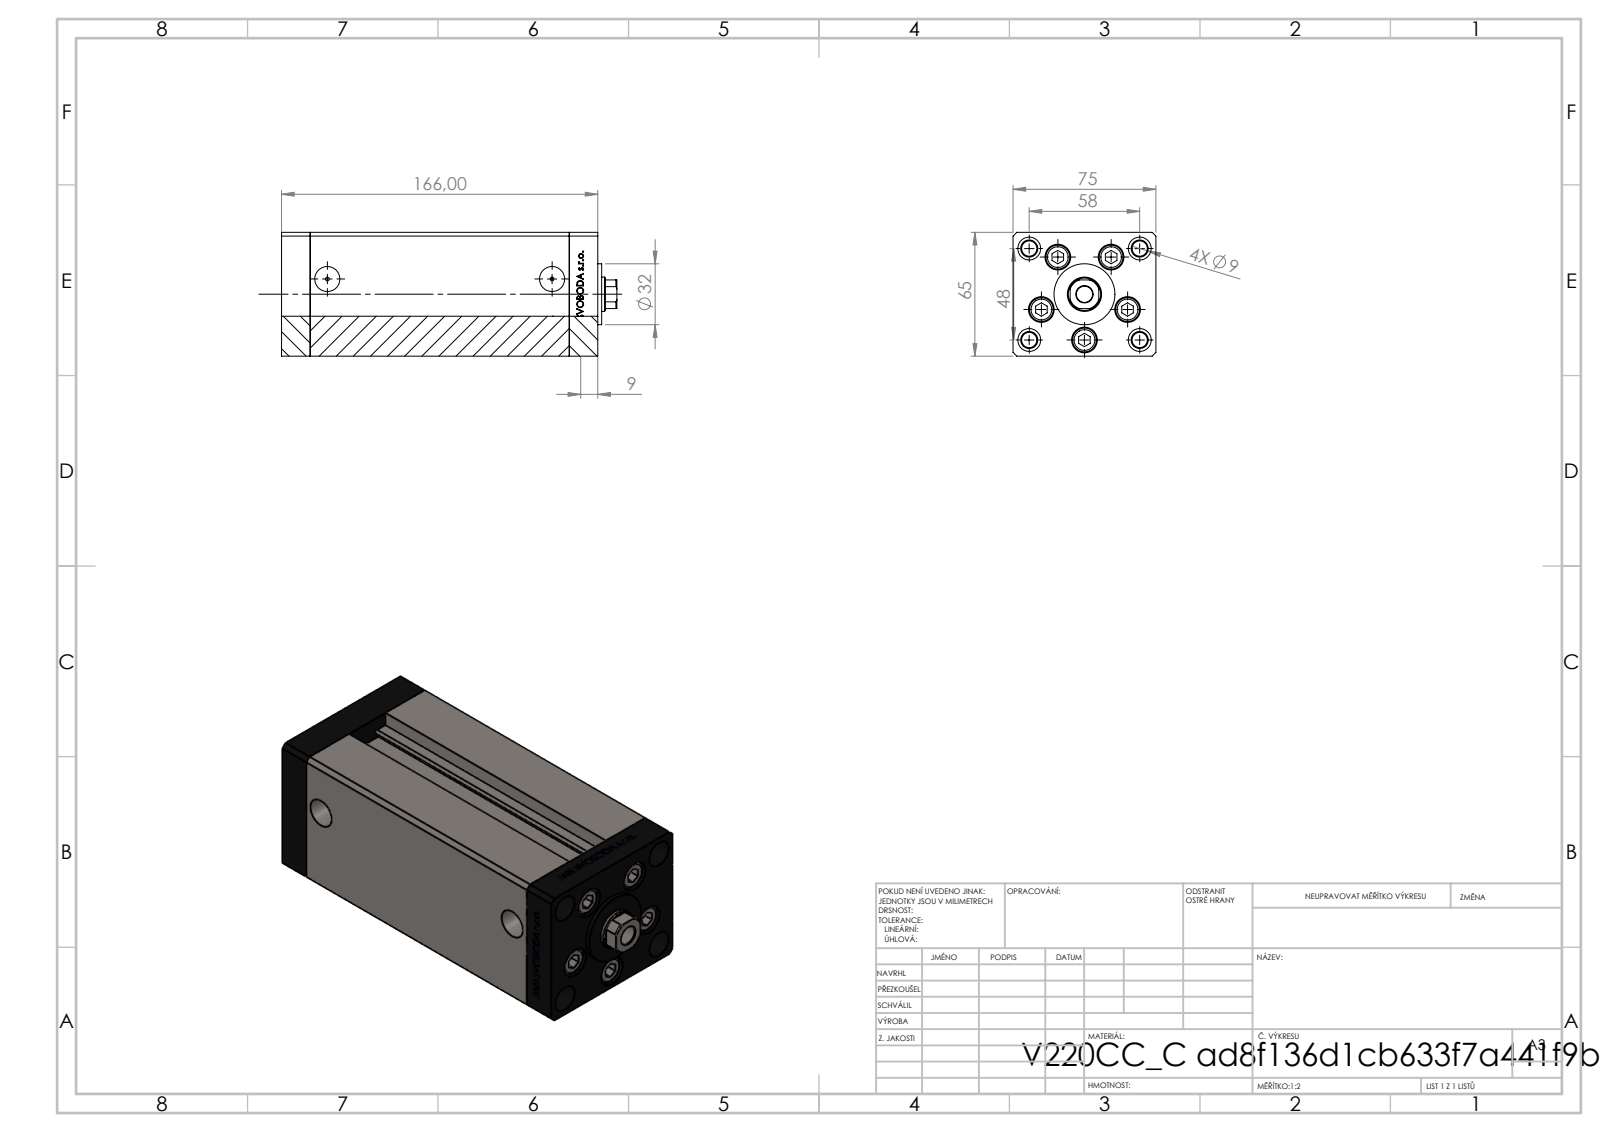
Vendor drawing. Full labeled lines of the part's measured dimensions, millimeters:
Part name (STEP PRODUCT): V220C FRONT; V220C_C MIDDLE; V220C_VC_C; V220C BACK_C (+1 more)
STEP written by: SolidWorks 2019 (CONFIG_CONTROL_DESIGN)
Units: millimetres
Bodies: 13 solids, 1169 faces (540 planar, 167 cylindrical, 462 other)
Overall size (bounding box): 176 × 75 × 65
Volume: 680 499 mm³ · Surface area: 142 517 mm²
Round holes (diameter × count): ⌀9 ×9, ⌀13.5 ×5, ⌀8 ×4, ⌀12 ×4, ⌀2 ×2, ⌀13.16 ×2, ⌀8.5 ×1, ⌀12.5 ×1, ⌀18 ×1
Round bosses / shafts (diameter × count): ⌀8 ×5, ⌀12.5 ×4, ⌀32 ×1
Partial cylindrical surfaces — rounded edges, fillets, slot ends (radius × count): R0.93 ×2, R8.5 ×1
Main face-to-face distances: 75, 65, 15, 136, 151, 166, 28, 142, 13, 9
Hole centre spacings: 24, 37.64, 15.67, 17.22, 27.71, 28.83, 29, 32.63
